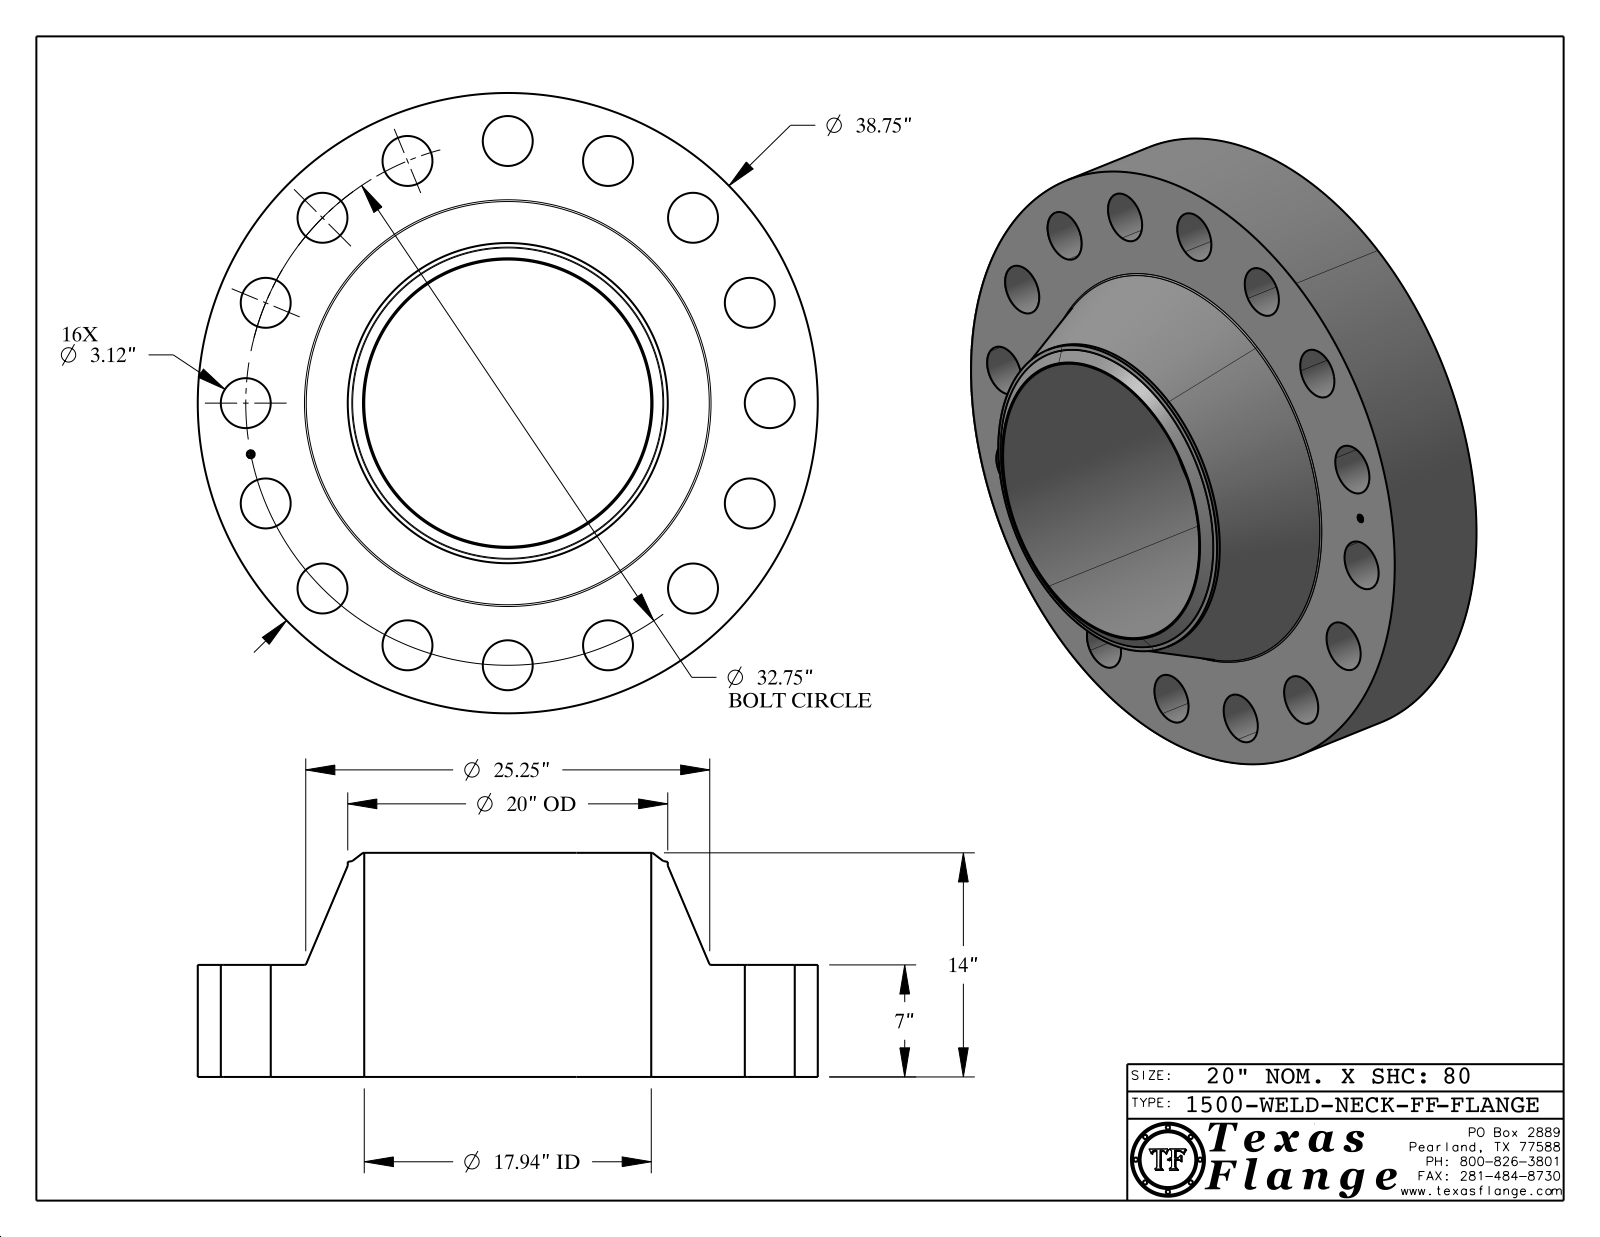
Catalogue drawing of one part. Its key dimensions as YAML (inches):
part_name: "1500-WELD-NECK-FF"
step_written_by: "CATIA V5 STEP AP214 (AUTOMOTIVE_DESIGN)"
units: inches
bodies: {solids: 1, faces: 436, planar: 368, cylindrical: 58, other: 10}
overall_size: [38.75, 38.75, 14]
volume: 6596
surface_area: 4663
round_holes:
  - {diameter: 3.12, count: 16}
  - {diameter: 0.495, count: 1}
  - {diameter: 17.938, count: 1}
round_bosses_or_shafts:
  - {diameter: 0.03, count: 8}
  - {diameter: 38.75, count: 1}
  - {diameter: 20, count: 1}
  - {diameter: 0.39, count: 1}
face_to_face_distances: [7, 14, 6.985, 0.015, 7.015, 0.148, 0.145, 0.027, 0.096, 0.123]
hole_center_spacings: [18.195, 16.375, 12.533, 23.157, 30.257, 6.389, 6.389, 27.23]
